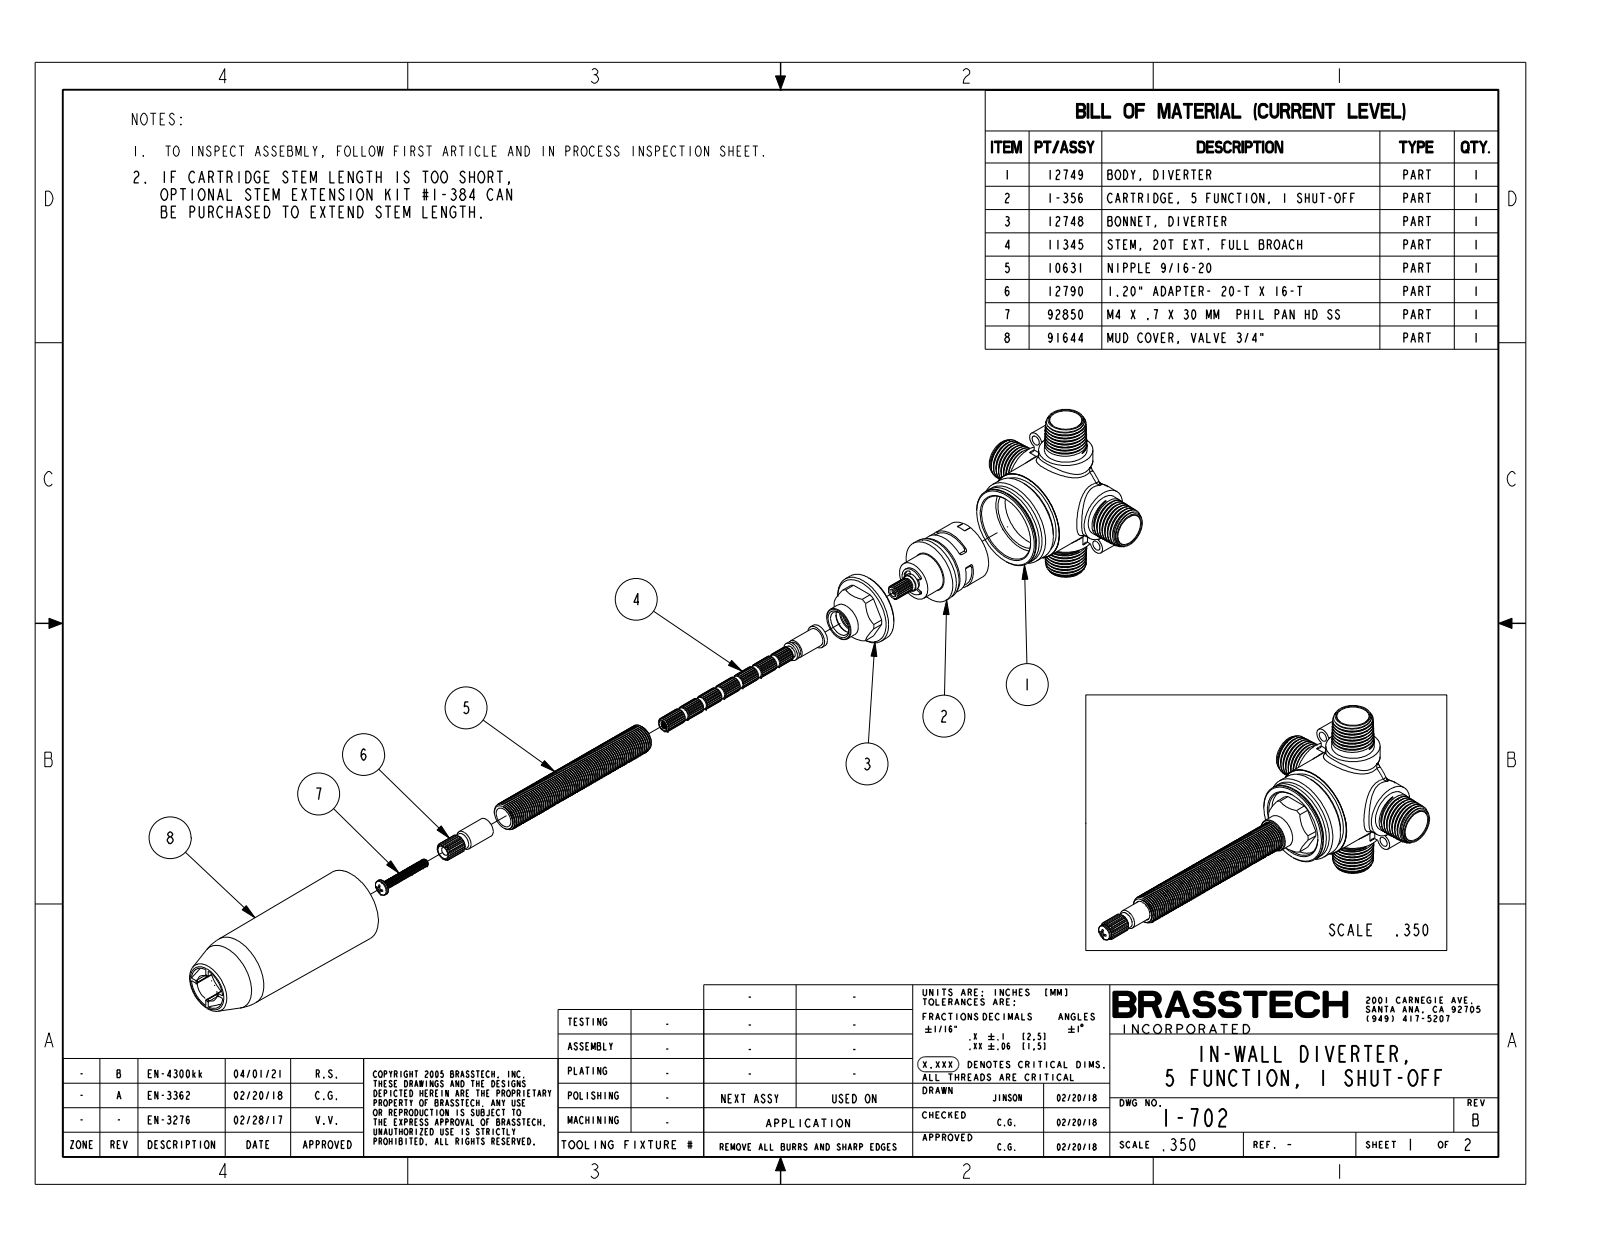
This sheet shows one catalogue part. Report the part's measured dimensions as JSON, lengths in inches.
{"part_name": "1-702", "step_written_by": "CREO PARAMETRIC BY PTC INC, 2018400 (AUTOMOTIVE_DESIGN)", "units": "inches", "bodies": {"solids": 1, "faces": 924, "planar": 174, "cylindrical": 442, "other": 308}, "overall_size": [7.574, 3.543, 3.543], "volume_in3": 7.375, "surface_area_in2": 53.67, "round_holes": [[0.197, 2], [0.394, 2], [0.585, 2], [0.63, 2], [0.172, 1], [0.33, 1], [1.805, 1]], "round_bosses_or_shafts": [[1.063, 2], [1.811, 1], [1.732, 1], [1.634, 1], [0.669, 1], [0.563, 1], [0.391, 1], [0.325, 1]], "partial_cylinders_radius": [[0.069, 13], [0.157, 5], [0.167, 2], [0.246, 2], [0.137, 1], [0.164, 1], [0.185, 1], [0.549, 1]], "face_to_face_distances": [1.949, 2.087, 0.157, 1.929, 0.02, 0.177, 2.106, 1.358, 0.591, 0.343], "hole_center_spacings": [1.191, 2.382]}
